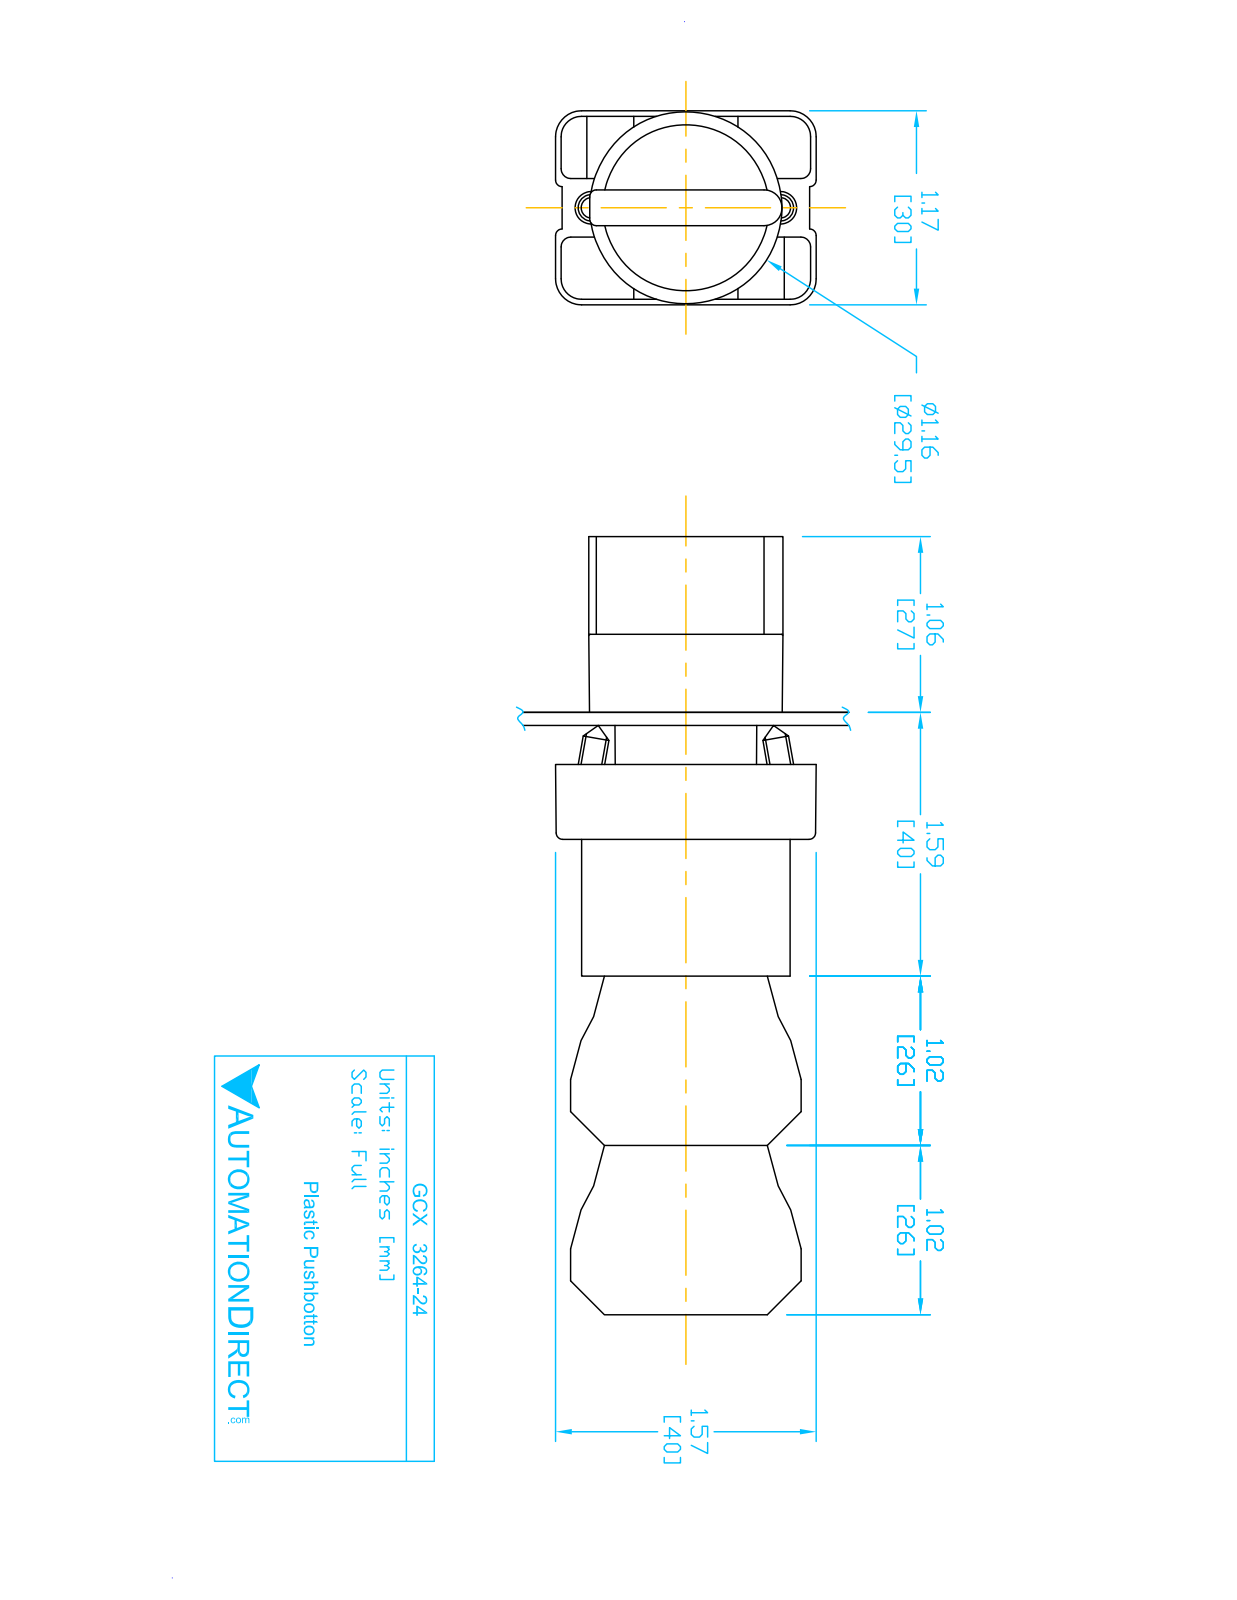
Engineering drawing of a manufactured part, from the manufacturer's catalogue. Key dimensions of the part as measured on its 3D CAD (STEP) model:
Part name (STEP PRODUCT): ECX1050; ecx1030; GCX3264-24L; GCX3264L OPERATOR (+2 more)
STEP written by: SolidWorks 2016 (AUTOMOTIVE_DESIGN)
Units: inches
Bodies: 11 solids, 724 faces (488 planar, 193 cylindrical, 43 other)
Overall size (bounding box): 4.677 × 1.581 × 1.177
Volume: 4.751 in³ · Surface area: 59.22 in²
Round holes (diameter × count): ⌀0.079 ×4, ⌀0.087 ×2, ⌀0.124 ×2, ⌀0.13 ×2, ⌀0.197 ×1, ⌀0.469 ×1, ⌀0.878 ×1, ⌀0.888 ×1, ⌀1.024 ×1
Round bosses / shafts (diameter × count): ⌀0.157 ×4, ⌀1.175 ×1, ⌀1.004 ×1, ⌀0.945 ×1, ⌀0.856 ×1, ⌀0.78 ×1, ⌀0.504 ×1
Partial cylindrical surfaces — rounded edges, fillets, slot ends (radius × count): R0.059 ×24, R0.041 ×12, R0.124 ×12, R0.157 ×12, R0.039 ×9, R0.02 ×2, R0.063 ×2, R0.079 ×2
Main face-to-face distances: 0.579, 0.593, 1.024, 1.171, 0.014, 0.827, 1.85, 3.043, 2.02, 1.193
Hole centre spacings: 0.236, 1.003, 0.974, 0.472, 0.539, 0.544, 1.083, 0.484
